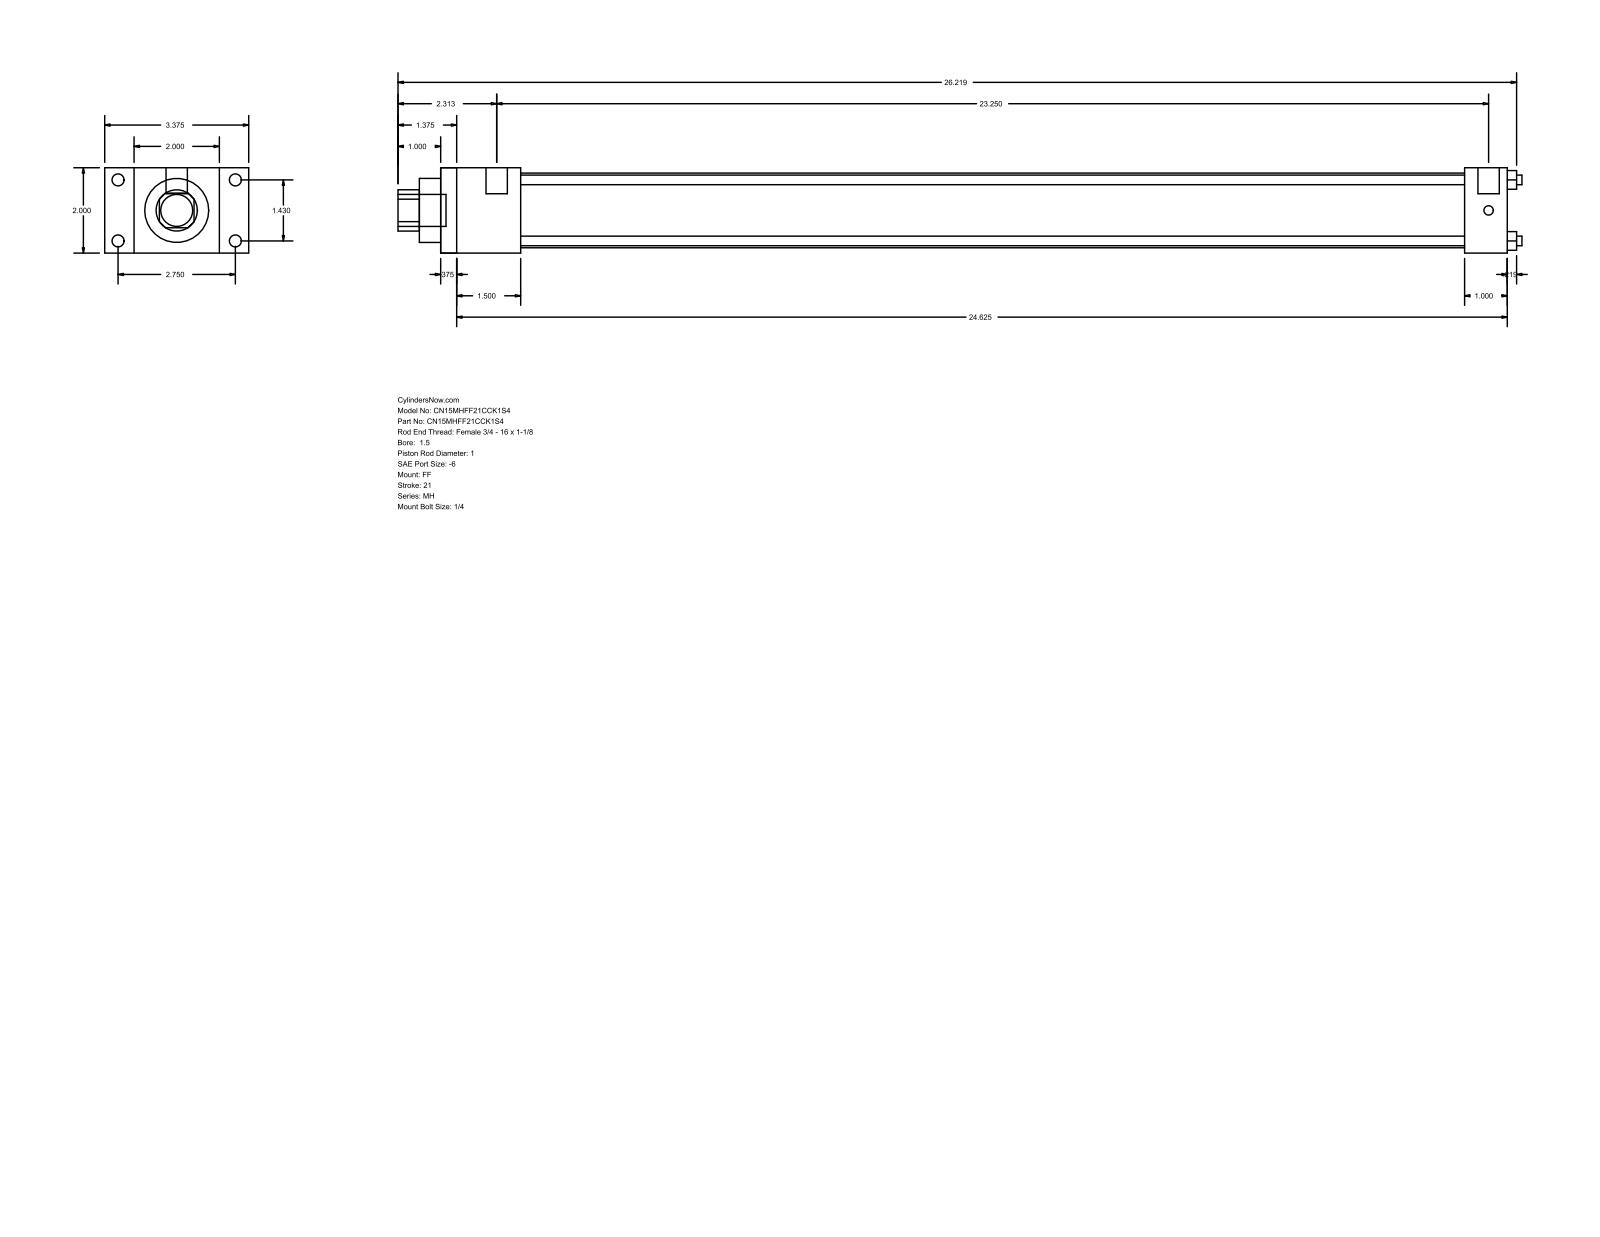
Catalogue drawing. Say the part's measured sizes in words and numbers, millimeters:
The part is named "MH_FF__0150_1". Its 3-D file was written by "GSSL Pune (CONFIG_CONTROL_DESIGN)". It is 0 solids with 92 faces: 64 planar, 28 cylindrical and 0 other. Overall it measures 669.13 by 85.72 by 50.8 millimeters. Round holes: 4 of diameter 5.71, 1 of diameter 25.4, 1 of diameter 38.1, 1 of diameter 44.45. Round bosses or shafts: 4 of diameter 7.14, 4 of diameter 5.56, 2 of diameter 12.7, 1 of diameter 19.05. Partial cylindrical surfaces (rounded edges, fillets, slot ends): 1 of radius 12.29. The main face-to-face distances are 50.8, 635, 9.52, 625.48, 25.4, 17.46, 68.26, 47.63, 38.11, 587.37. The hole center spacings are 25.68, 36.32, 51.36.
